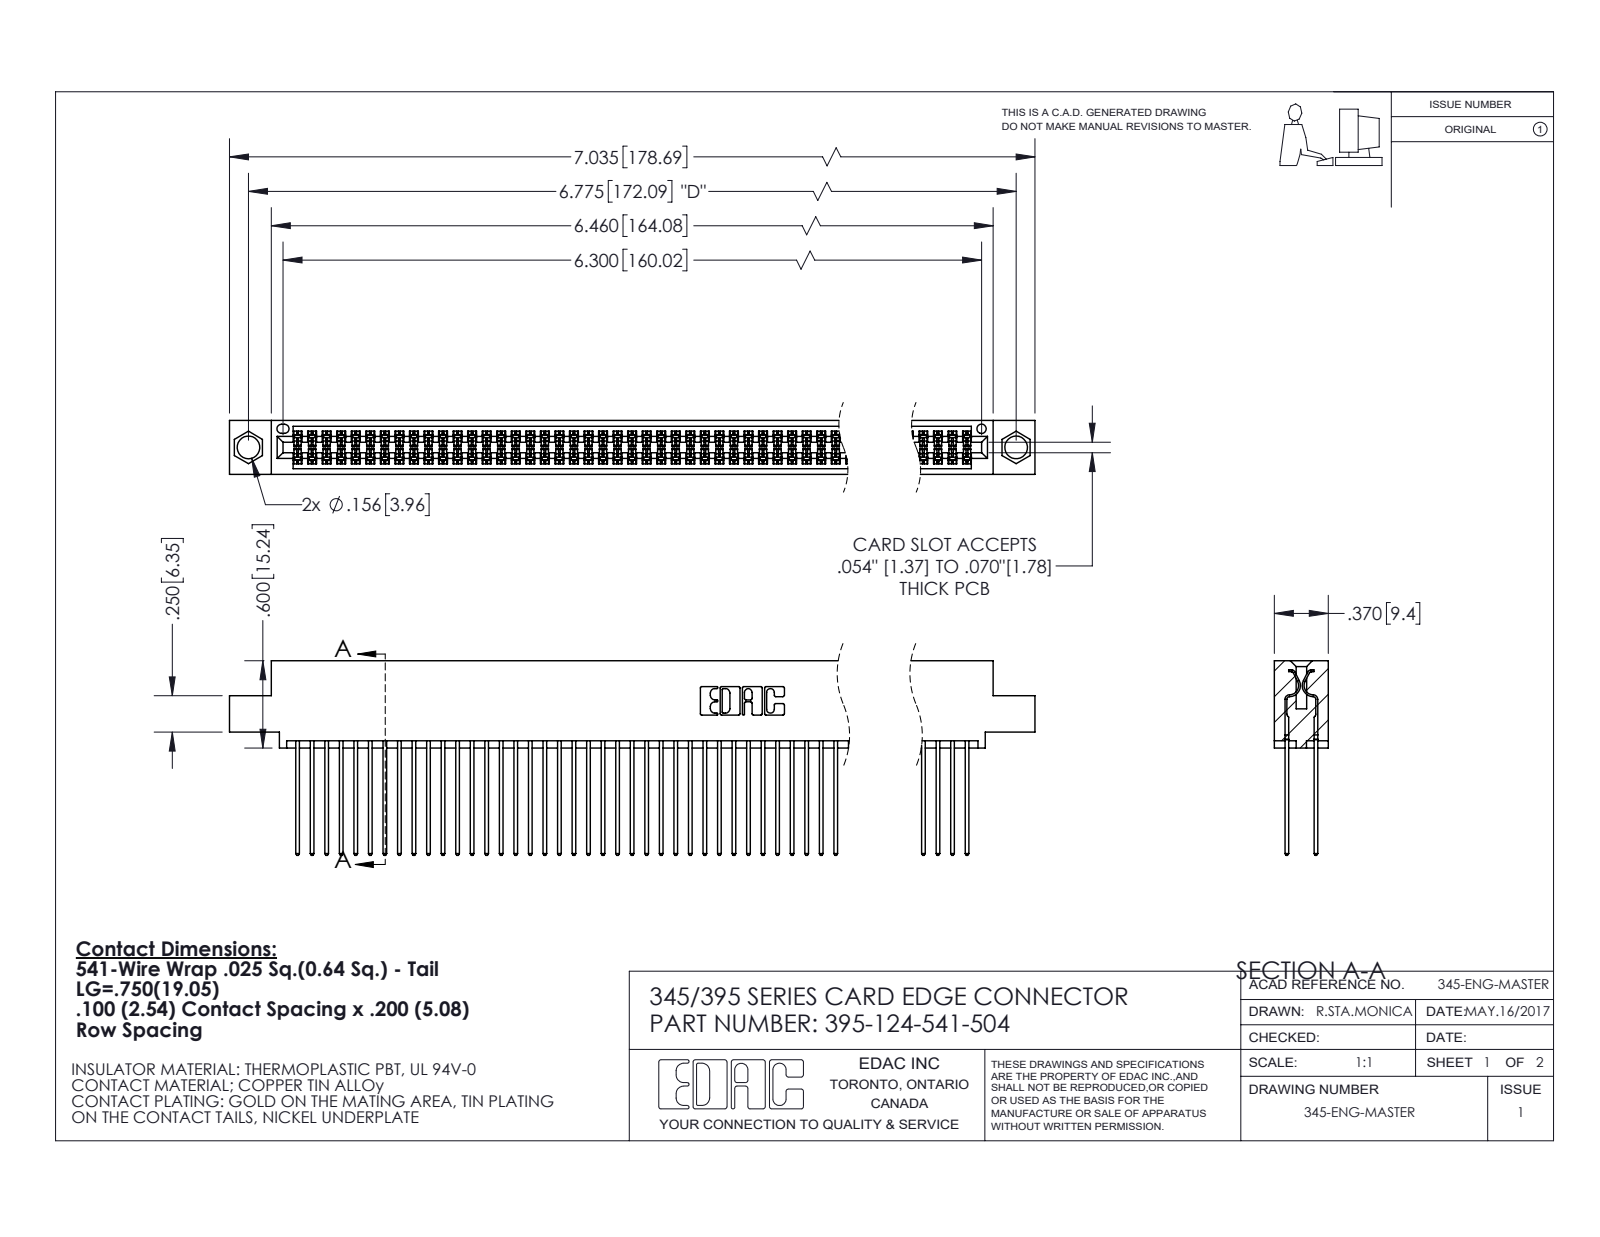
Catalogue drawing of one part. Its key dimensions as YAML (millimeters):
part_name: "345 Part_0.110 Offset - 0.156 Dia-TI; 345-292-001_345-293-141; 395-124-541-504"
step_written_by: "SolidWorks 2020 (CONFIG_CONTROL_DESIGN)"
units: millimeters
bodies: {solids: 125, faces: 6344, planar: 4190, cylindrical: 2154, other: 0}
overall_size: [178.7, 34, 9.4]
volume: 18070
surface_area: 30390
round_holes:
  - {diameter: 4, count: 2}
  - {diameter: 1.6, count: 1}
partial_cylinders:
  - {radius: 0.2, count: 186}
  - {radius: 0.3, count: 124}
  - {radius: 0.3, count: 22}
  - {radius: 0.2, count: 6}
  - {radius: 0.8, count: 6}
  - {radius: 0.7, count: 3}
  - {radius: 0.4, count: 2}
  - {radius: 0.5, count: 2}
face_to_face_distances: [7.6, 1.8, 5.1, 2.5, 6.9, 0.6, 5.7, 9.4, 4.4, 3.8]
hole_center_spacings: [6.9, 166.1, 172.1]
